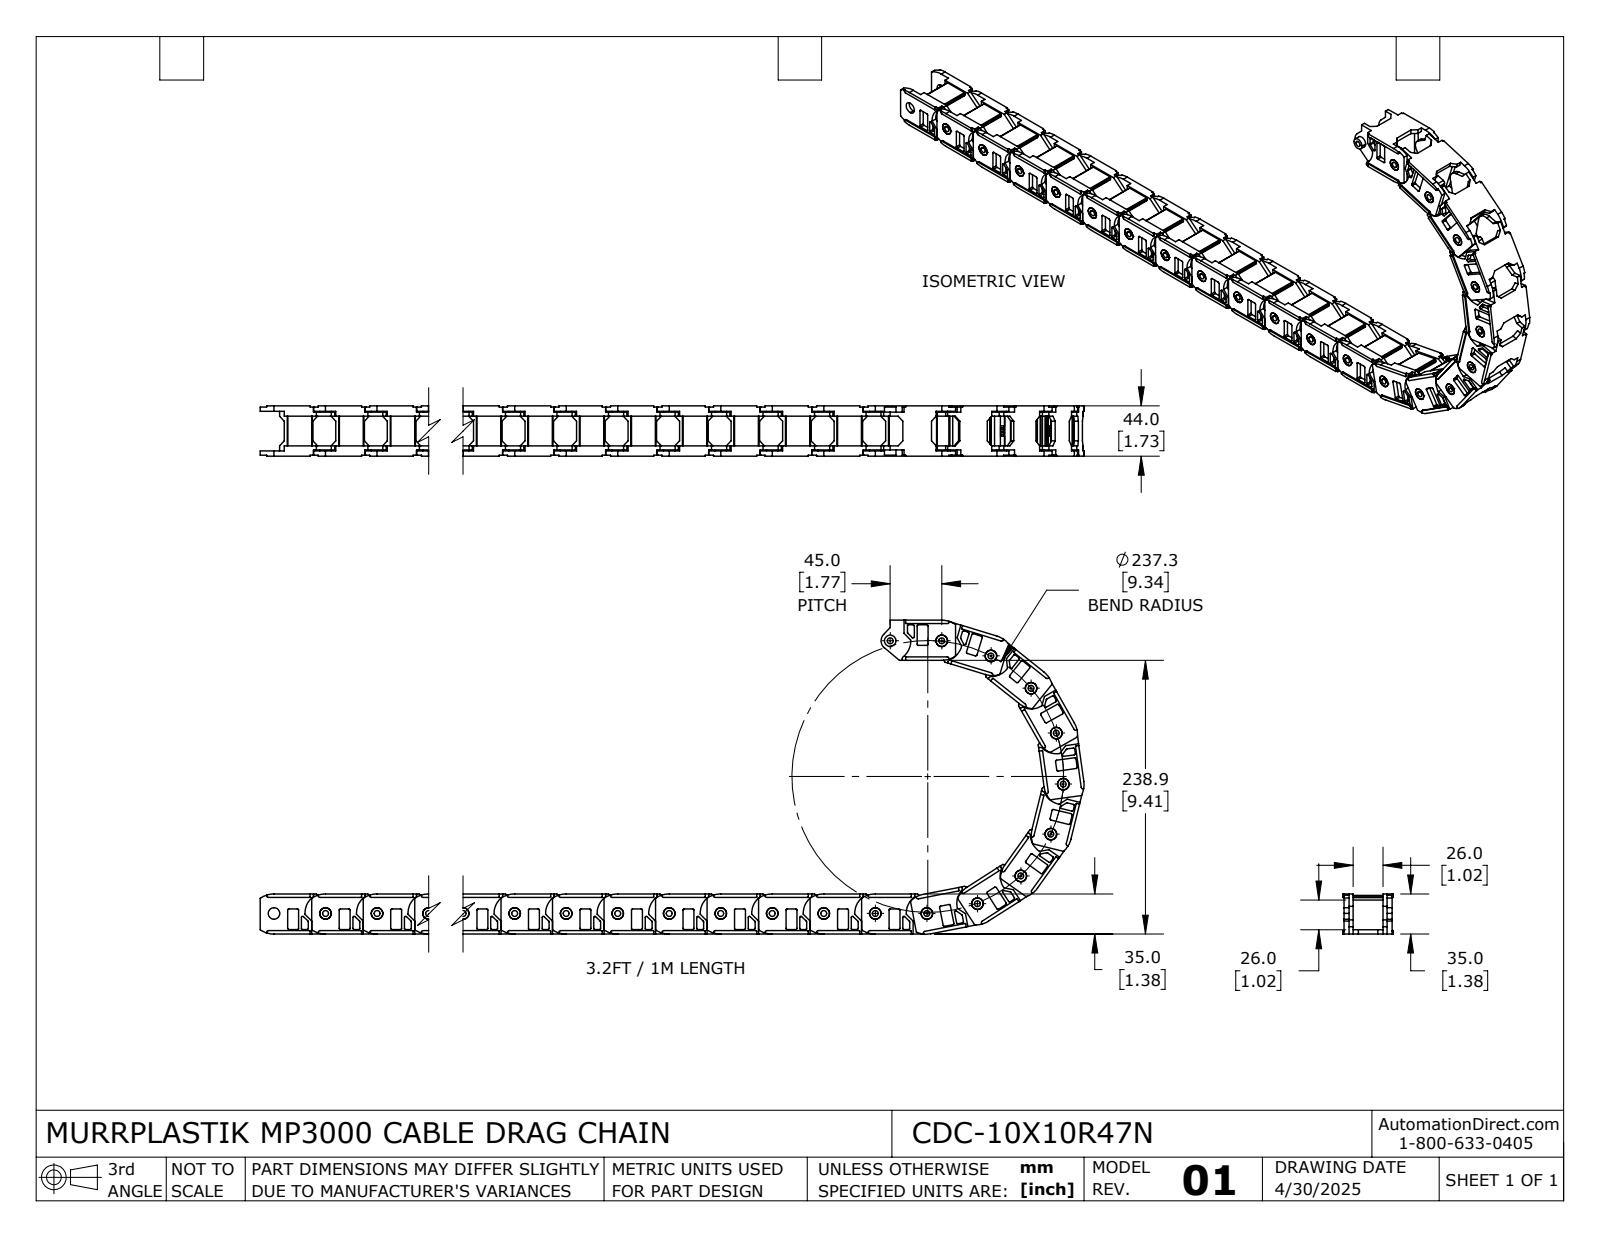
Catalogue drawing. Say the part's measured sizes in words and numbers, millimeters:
The part is named "CDC-10X10R47N". Its 3-D file was written by "SolidWorks 2024 (AUTOMOTIVE_DESIGN)". It is 22 solids with 3344 faces: 2244 planar, 1100 cylindrical and 0 other. Overall it measures 733.99 by 274 by 44 millimeters. Its volume is 546 930 cubic millimeters and its surface area 321 003 square millimeters. Round holes: 22 of diameter 5.1, 22 of diameter 10.1. Round bosses or shafts: 22 of diameter 10. Partial cylindrical surfaces (rounded edges, fillets, slot ends): 176 of radius 1, 88 of radius 0.5, 44 of radius 1.5, 44 of radius 2, 44 of radius 21, 22 of radius 2.8, 22 of radius 8, 22 of radius 18. The main face-to-face distances are 34, 8, 33.8, 26, 4, 30.3, 3.7, 38.3, 4.3, 3.5. The hole center spacings are 44.98, 45, 89.96, 134.94, 89.98, 179.92, 44.93, 44.96.
